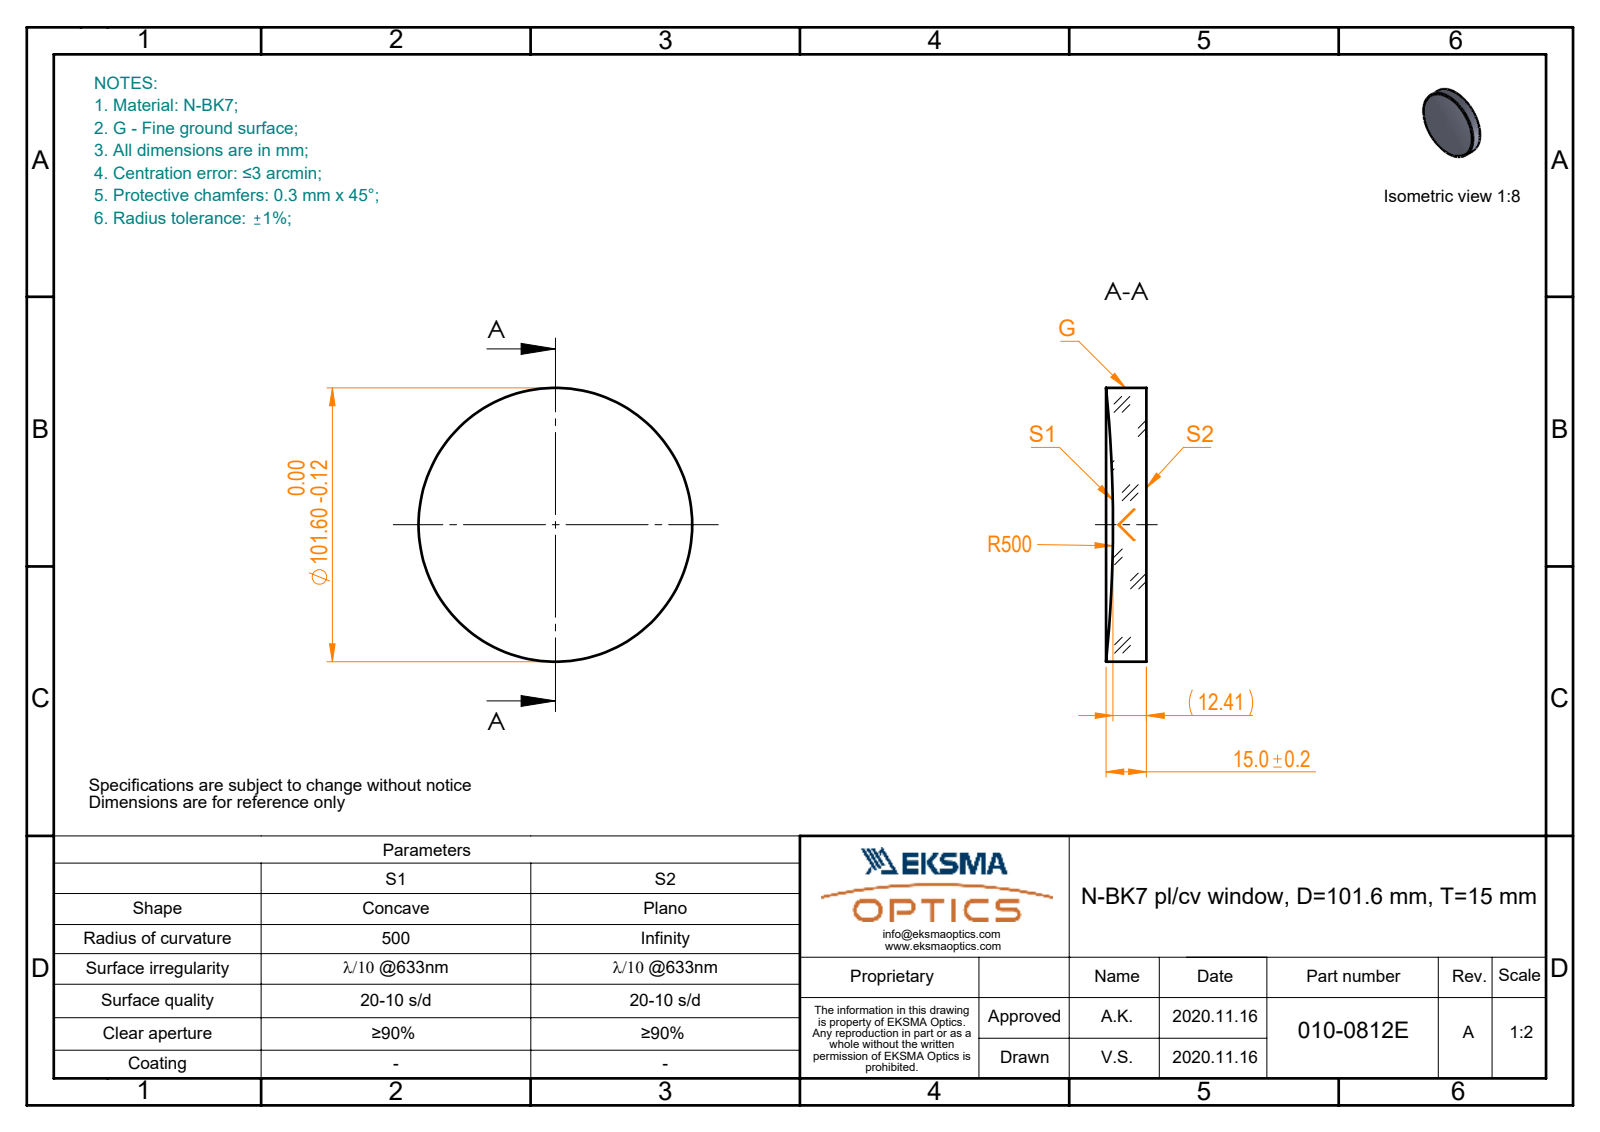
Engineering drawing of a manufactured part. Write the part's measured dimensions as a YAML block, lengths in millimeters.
part_name: "010-0812E_N-BK7_PCV_window"
step_written_by: "SolidWorks 2019 (CONFIG_CONTROL_DESIGN)"
units: millimeters
bodies: {solids: 1, faces: 5, planar: 1, cylindrical: 2, other: 2}
overall_size: [101.6, 101.6, 15]
volume: 111113
surface_area: 21023
round_bosses_or_shafts:
  - {diameter: 101.6, count: 1}
